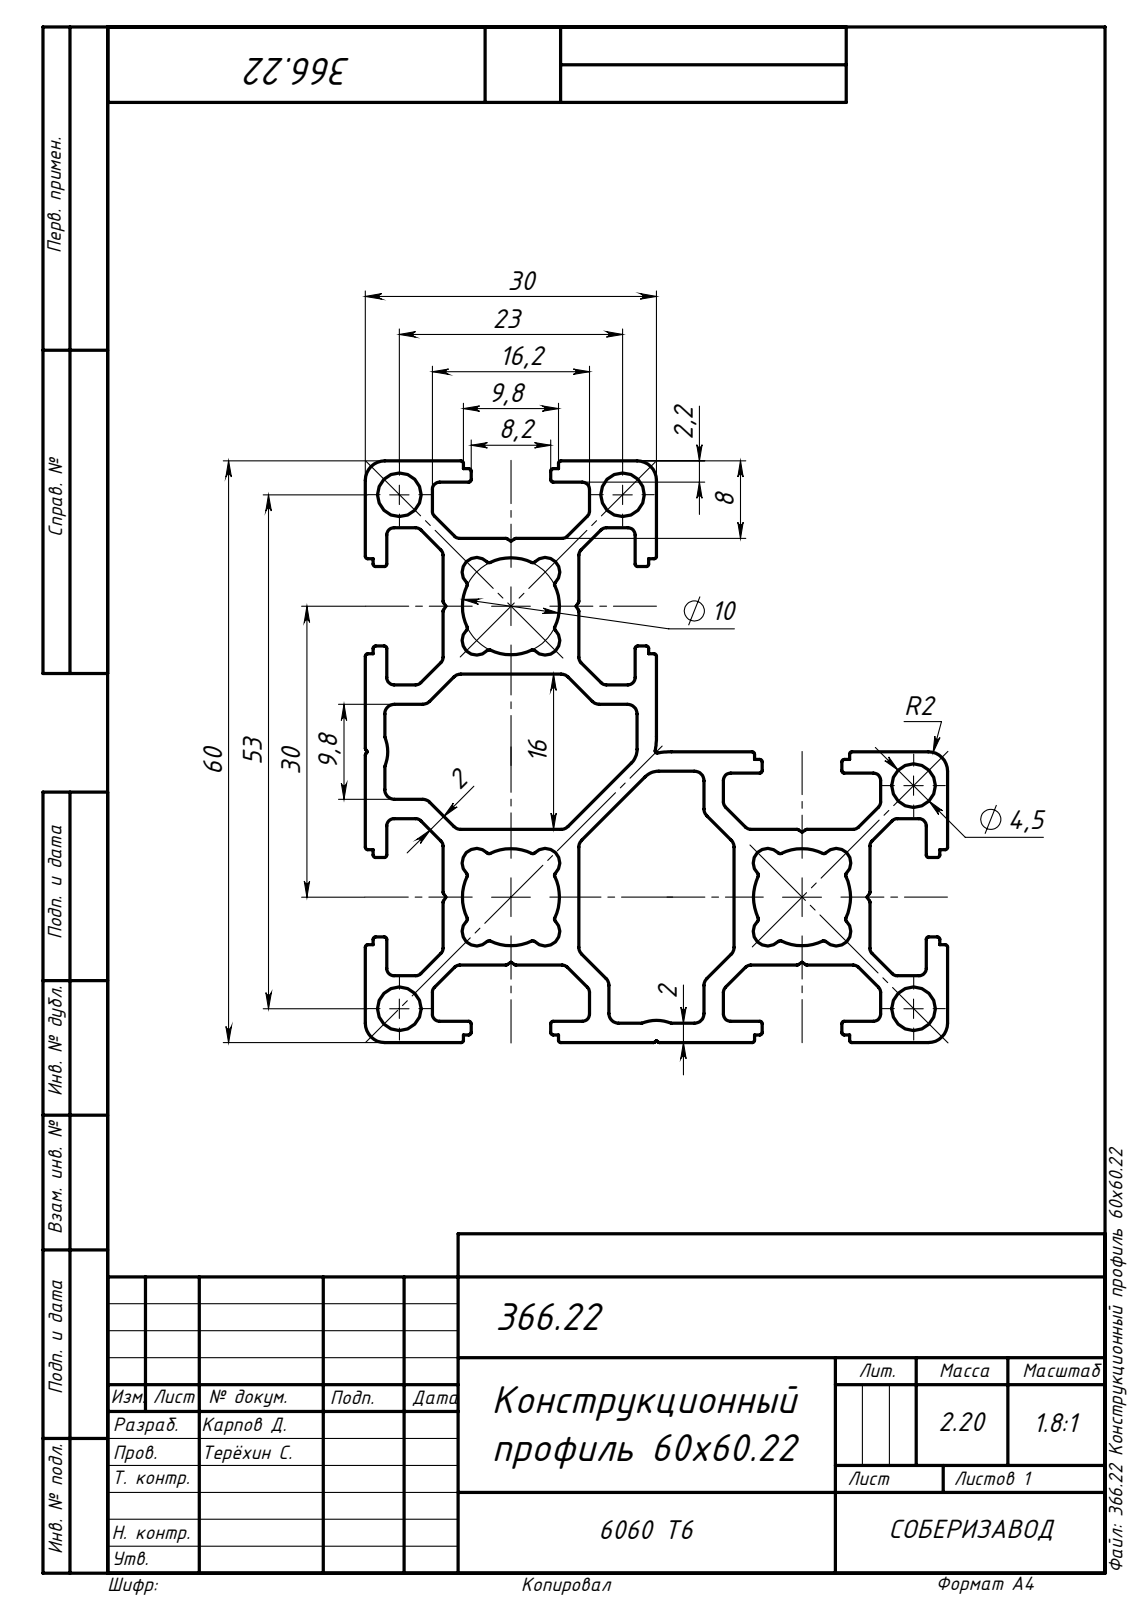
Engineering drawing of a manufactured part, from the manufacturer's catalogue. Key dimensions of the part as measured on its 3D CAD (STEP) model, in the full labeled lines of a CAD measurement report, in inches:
Part name (STEP PRODUCT): 366.22 Конструкционный профиль 60х60.22
STEP written by: SolidWorks 2017 (AUTOMOTIVE_DESIGN)
Units: inches
Bodies: 1 solid, 399 faces (178 planar, 221 cylindrical, 0 other)
Overall size (bounding box): 4.724 × 2.362 × 2.362
Volume: 5.966 in³ · Surface area: 150.1 in²
Round holes (diameter × count): ⌀0.177 ×5
Partial cylindrical surfaces — rounded edges, fillets, slot ends (radius × count): R0.01 ×92, R0.03 ×48, R0.039 ×20, R0.059 ×12, R0.079 ×7, R0.197 ×3, R0.157 ×2, R0.315 ×2
Main face-to-face distances: 1.181, 0.866, 0.315, 0.079, 0.551, 1.496, 2.047, 0.087, 1.094, 0.228
Hole centre spacings: 0.906, 2.087, 2.275, 2.398, 1.67, 2.951
